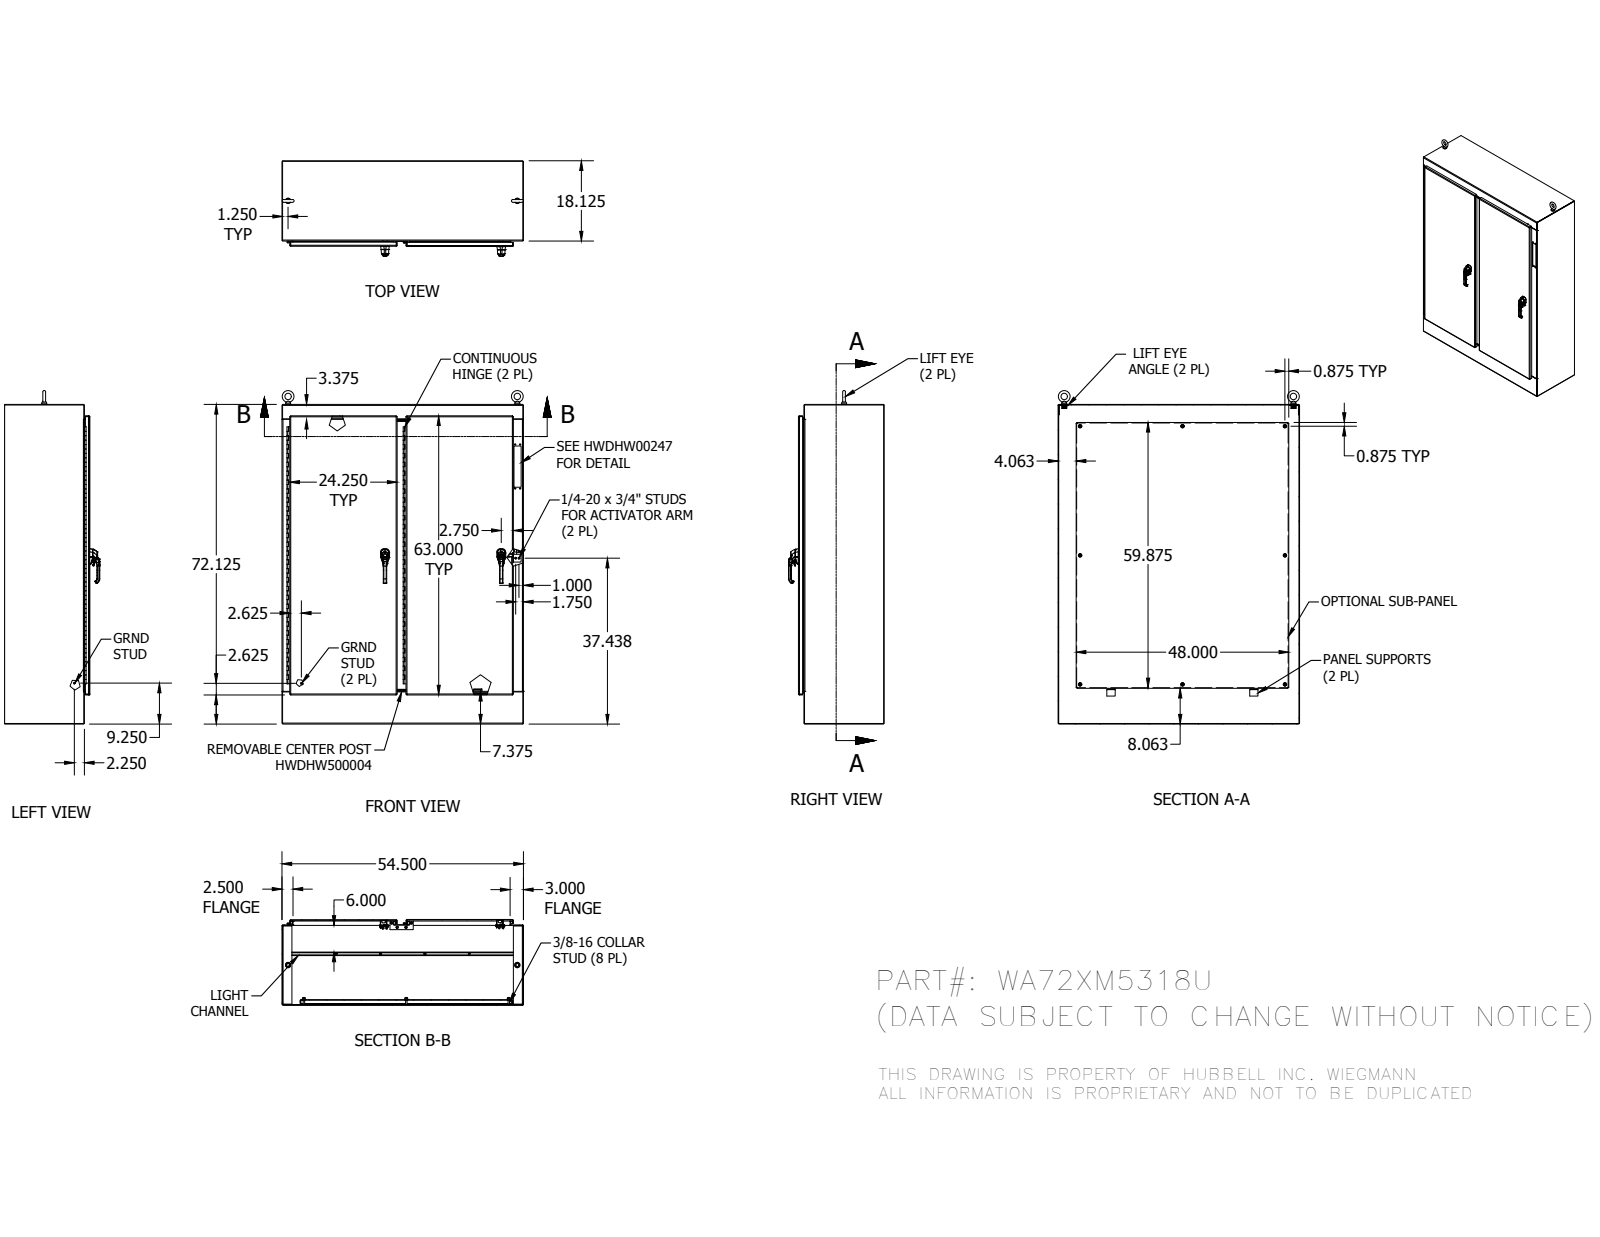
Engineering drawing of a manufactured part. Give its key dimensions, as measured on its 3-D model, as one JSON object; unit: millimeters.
{"part_name": "WA72XM53U_BACK; 3889; 349104; HFW3878 (+8 more)", "step_written_by": "Autodesk Inventor 2014 (AUTOMOTIVE_DESIGN)", "units": "millimeters", "bodies": {"solids": 223, "faces": 8808, "planar": 4094, "cylindrical": 2886, "other": 1828}, "overall_size": [1911.29, 1384.3, 548.73], "volume_mm3": 29400000, "surface_area_mm2": 19100000, "round_holes": [[6.35, 18], [9.52, 18], [7.02, 16], [7.14, 10], [4.83, 8], [5.08, 8], [7.33, 8], [7.8, 8], [7.94, 8], [8.51, 8], [9.65, 8], [3.96, 6]], "round_bosses_or_shafts": [[6.35, 20], [8.38, 18], [15.88, 13], [9.52, 12], [8.56, 12], [14.29, 9], [7.11, 8], [25.4, 7]], "partial_cylinders_radius": [[0.5, 359], [0.3, 215], [0.51, 192], [0.47, 42], [1.27, 32], [2, 28], [1.59, 24], [1.5, 23]], "face_to_face_distances": [3.17, 3.18, 1.59, 31.23, 29.64, 4.77, 488.43, 485.26, 486.84, 483.67], "hole_center_spacings": [1371.28, 1390.33, 1.59, 1380.81, 1390.34, 1399.85, 9.66, 40.66]}
